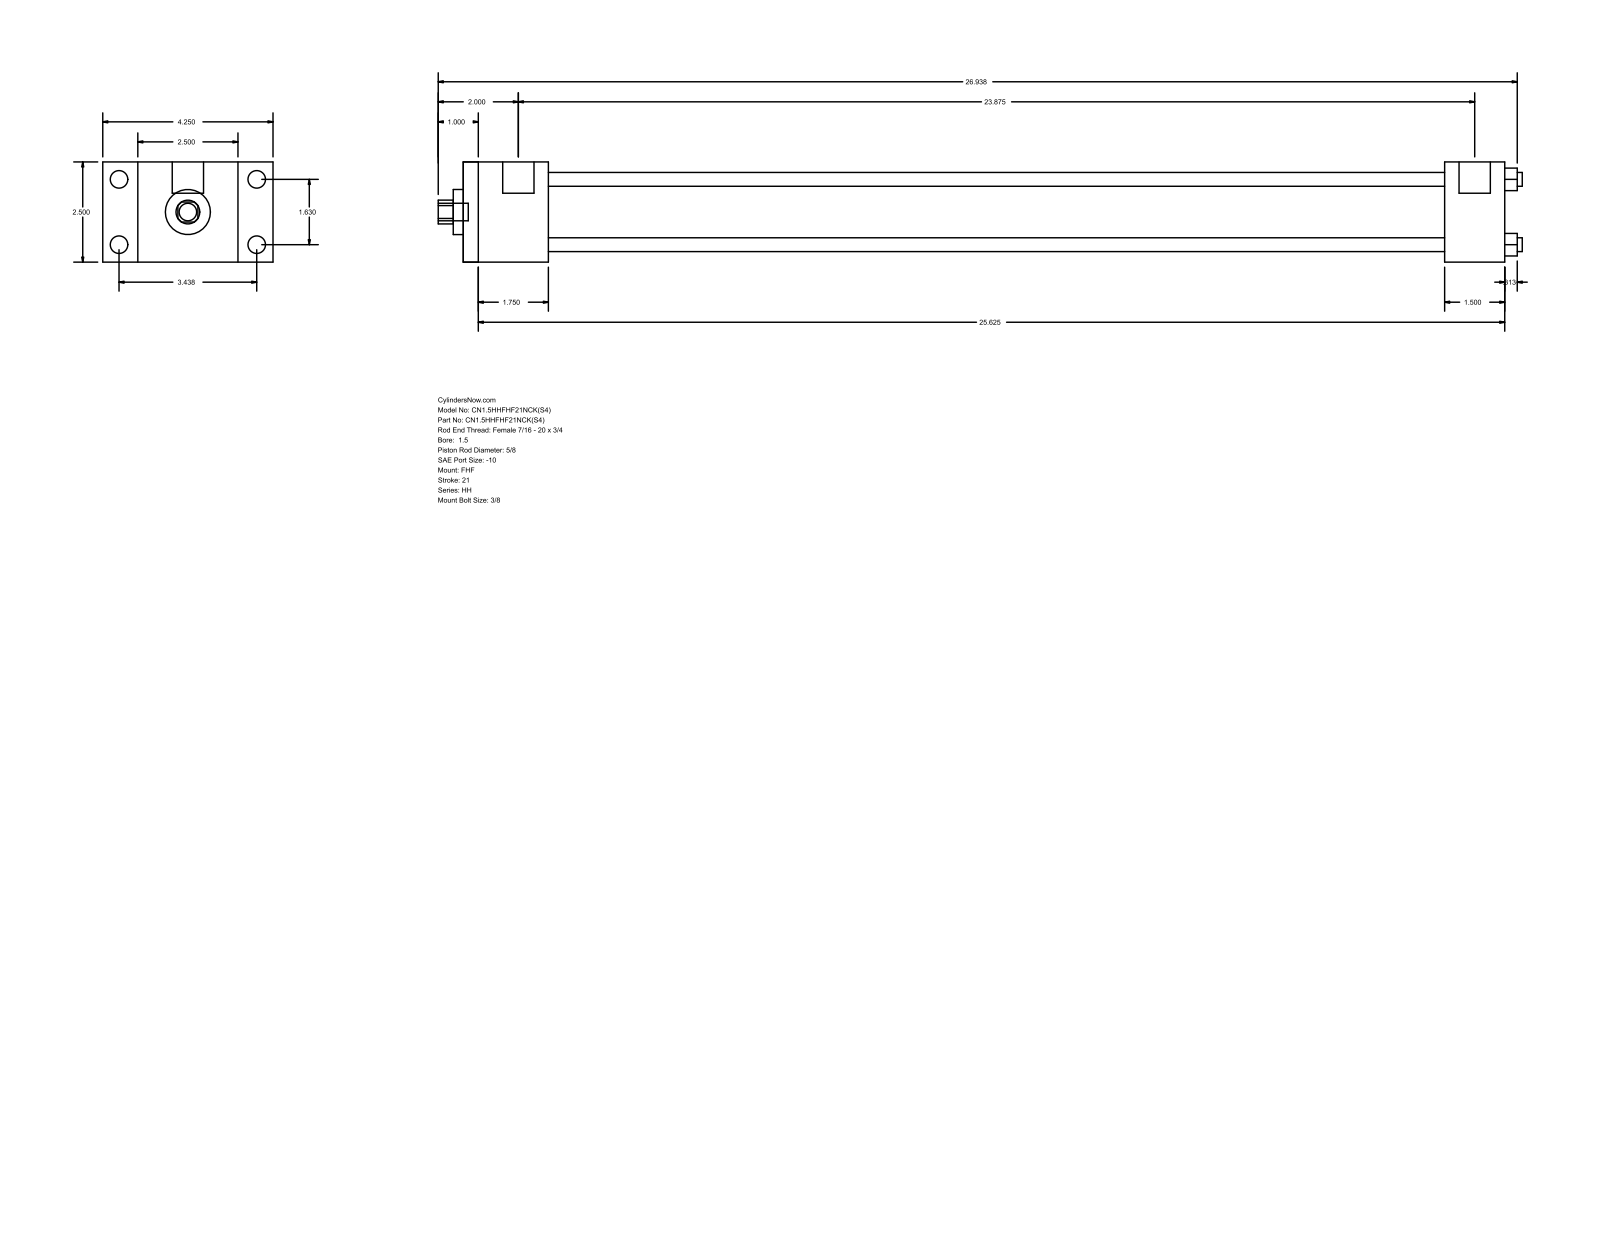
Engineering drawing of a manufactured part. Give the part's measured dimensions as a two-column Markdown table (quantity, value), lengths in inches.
| quantity | value |
| --- | --- |
| part name | HH_FHF__0150_0.625 |
| STEP written by | GSSL Pune (CONFIG_CONTROL_DESIGN) |
| units | inches |
| bodies | 0 solids, 88 faces (60 planar, 28 cylindrical, 0 other) |
| overall size | 27.063 × 4.25 × 2.5 |
| round holes (diameter × count) | 0.345 × 4, 0.625 × 1, 1.125 × 1, 1.75 × 1 |
| round bosses / shafts (diameter × count) | 0.438 × 4, 0.219 × 4, 0.781 × 2, 0.437 × 1 |
| partial cylindrical surfaces (radius × count) | 0.297 × 1 |
| main face-to-face distances | 2.5, 0.875, 3.375, 2.125, 4.25, 26, 23.875, 1.5, 24.5, 22.375 |
| hole center spacings | 1.152, 1.63, 2.305 |
